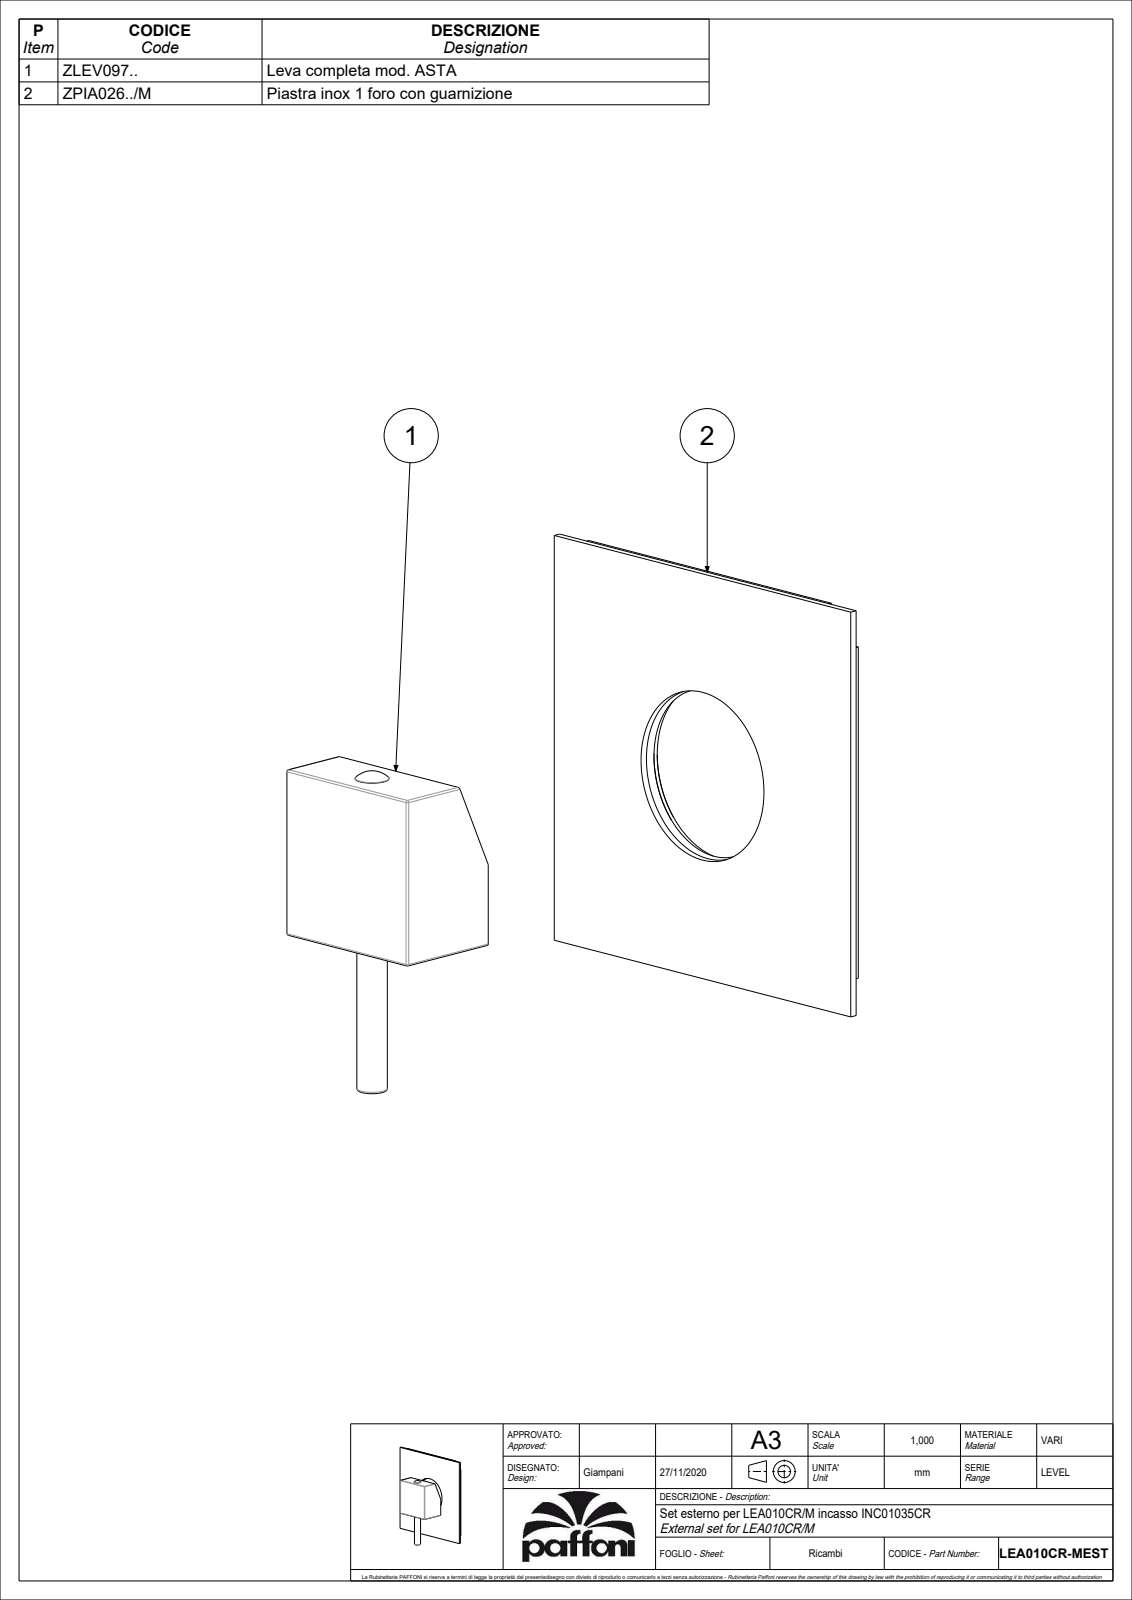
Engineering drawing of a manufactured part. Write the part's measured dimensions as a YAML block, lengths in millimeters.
part_name: "LEA010CR-MEST"
step_written_by: "CREO PARAMETRIC BY PTC INC, 2020044 (CONFIG_CONTROL_DESIGN)"
units: millimeters
bodies: {solids: 2, faces: 170, planar: 102, cylindrical: 40, other: 28}
overall_size: [117.5, 110, 39.5]
volume: 43391
surface_area: 41607
round_holes:
  - {diameter: 5.5, count: 1}
  - {diameter: 6, count: 1}
  - {diameter: 8.1, count: 1}
  - {diameter: 45.6, count: 1}
  - {diameter: 47.6, count: 1}
  - {diameter: 51.1, count: 1}
round_bosses_or_shafts:
  - {diameter: 54.6, count: 1}
  - {diameter: 8, count: 1}
  - {diameter: 5, count: 1}
partial_cylinders:
  - {radius: 0.5, count: 10}
face_to_face_distances: [2, 0.8, 2.8, 34.8, 45, 34, 32, 3, 32.5, 77.5]
